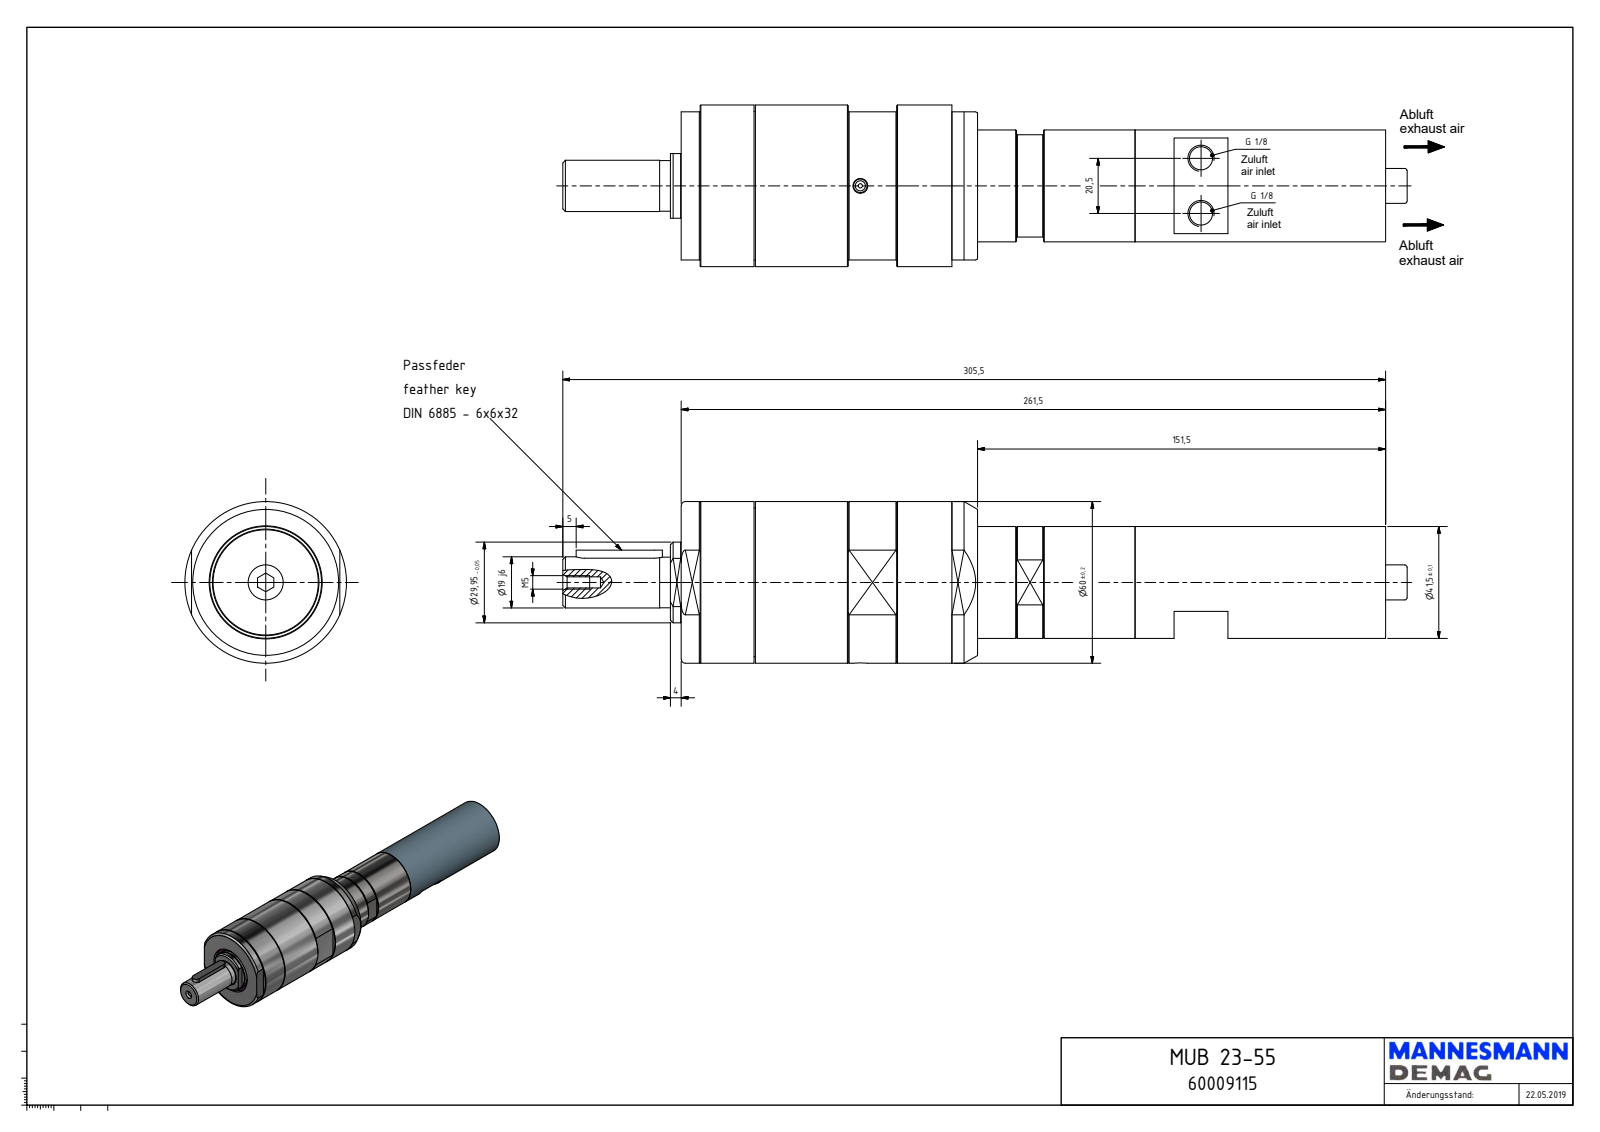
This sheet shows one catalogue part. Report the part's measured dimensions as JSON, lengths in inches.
{"part_name": "MUB 23-55_60009115", "step_written_by": "Autodesk Inventor 2018 (AUTOMOTIVE_DESIGN)", "units": "inches", "bodies": {"solids": 1, "faces": 181, "planar": 79, "cylindrical": 64, "other": 38}, "overall_size": [12.343, 2.362, 2.362], "volume_in3": 31.66, "surface_area_in2": 87.45, "round_holes": [[0.337, 2], [0.061, 1], [0.157, 1], [0.163, 1], [0.217, 1], [0.335, 1], [1.378, 1], [1.555, 1], [1.654, 1], [2.18, 1]], "round_bosses_or_shafts": [[2.362, 1], [2.172, 1], [1.634, 1], [1.535, 1], [1.535, 1], [1.179, 1], [0.748, 1], [0.74, 1]], "partial_cylinders_radius": [[0.063, 4], [0.039, 2], [0.079, 2], [0.098, 2], [0.118, 2], [0.315, 1], [0.319, 1], [0.496, 1]], "face_to_face_distances": [10.295, 4.331, 5.965, 2.165, 3.248, 3.091, 1.083, 9.213, 1.22, 2.874], "hole_center_spacings": [4.996, 0.807]}
